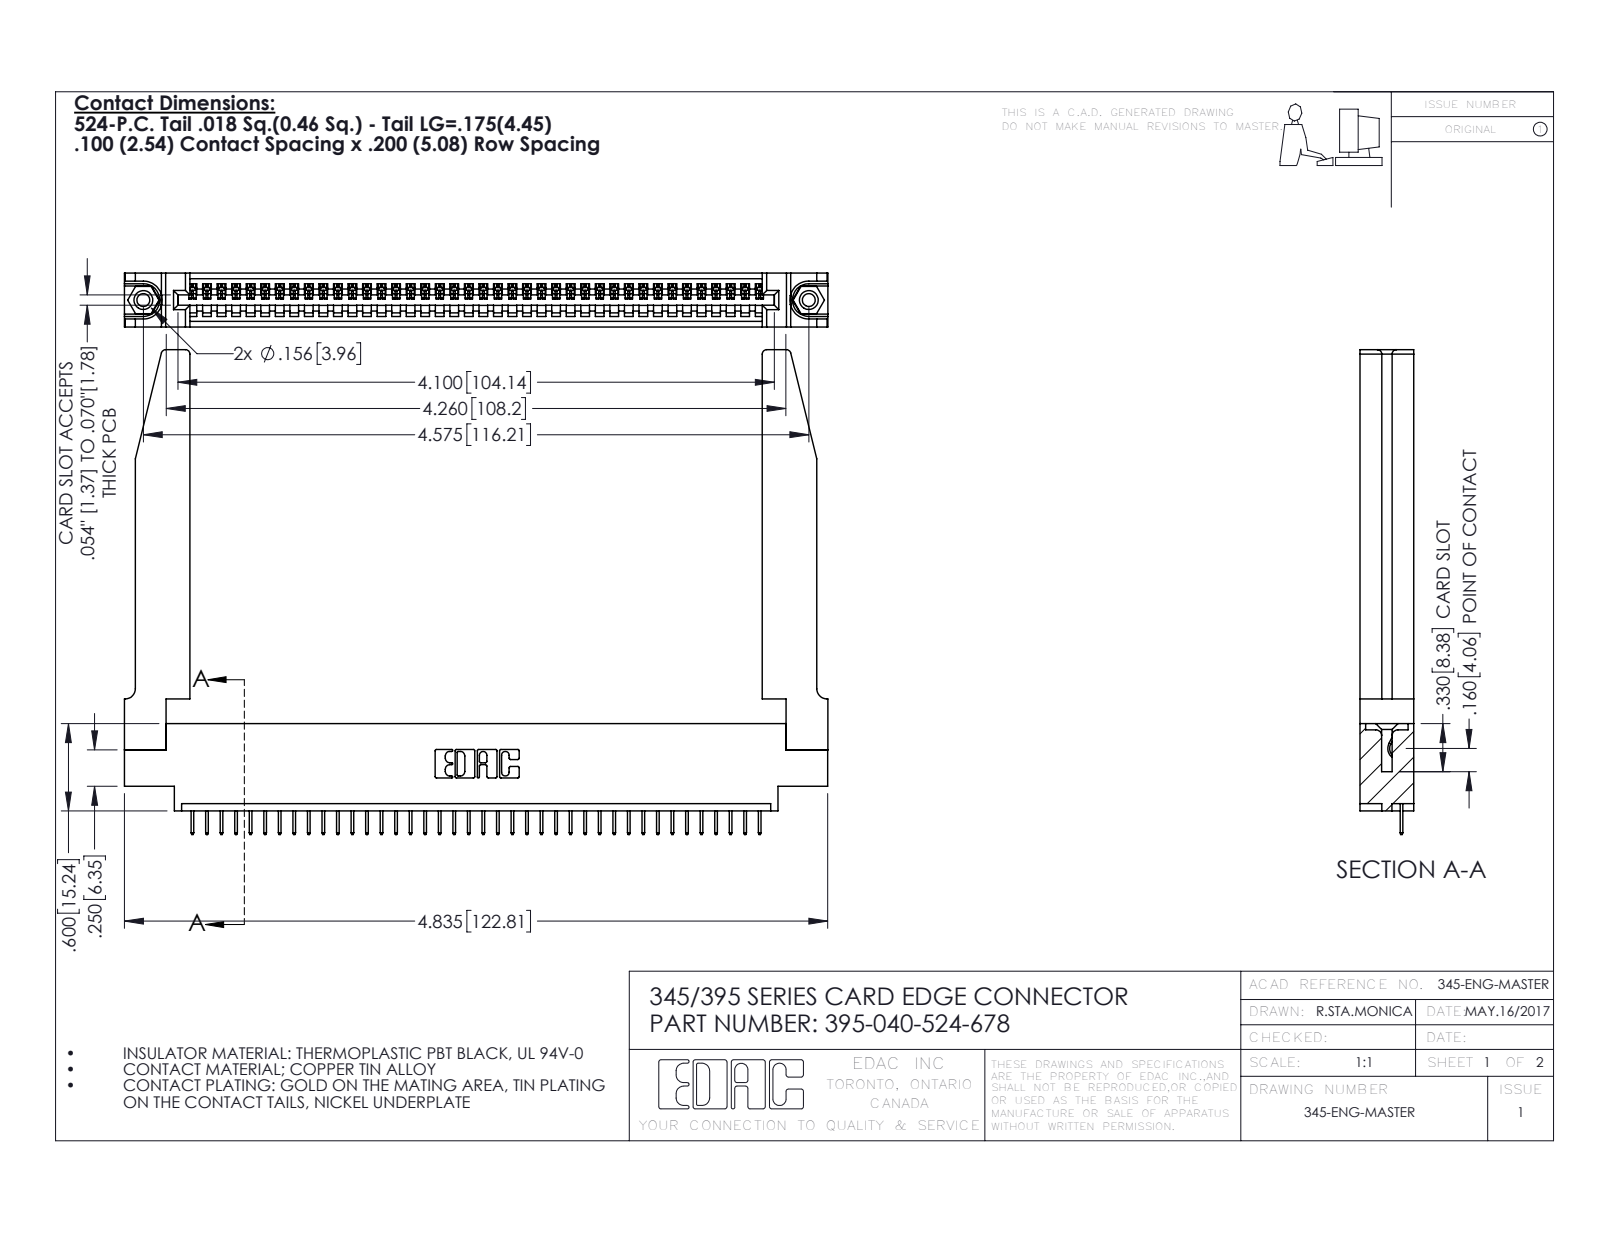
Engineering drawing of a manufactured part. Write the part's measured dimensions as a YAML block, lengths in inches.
part_name: "345-250-001_345-250-001-102; 395-040-524-678; 345 Part_0.170 Offset - 0.156 Dia-TH; 345-292-001_345-293-124 (+1 more)"
step_written_by: "SolidWorks 2016 (CONFIG_CONTROL_DESIGN)"
units: inches
bodies: {solids: 45, faces: 2844, planar: 2066, cylindrical: 726, other: 52}
overall_size: [4.836, 3.332, 0.37]
volume: 1.169
surface_area: 33.42
round_holes:
  - {diameter: 0.089, count: 2}
  - {diameter: 0.125, count: 2}
  - {diameter: 0.156, count: 2}
  - {diameter: 0.064, count: 1}
round_bosses_or_shafts:
  - {diameter: 0.155, count: 2}
partial_cylinders:
  - {radius: 0.006, count: 80}
  - {radius: 0.01, count: 22}
  - {radius: 0.03, count: 8}
  - {radius: 0.007, count: 6}
  - {radius: 0.031, count: 6}
  - {radius: 0.026, count: 3}
  - {radius: 0.031, count: 2}
  - {radius: 0.04, count: 2}
face_to_face_distances: [0.37, 0.072, 0.298, 0.098, 0.272, 0.025, 0.2, 0.225, 0.148, 0.15]
hole_center_spacings: [0.27, 4.339, 4.575]
